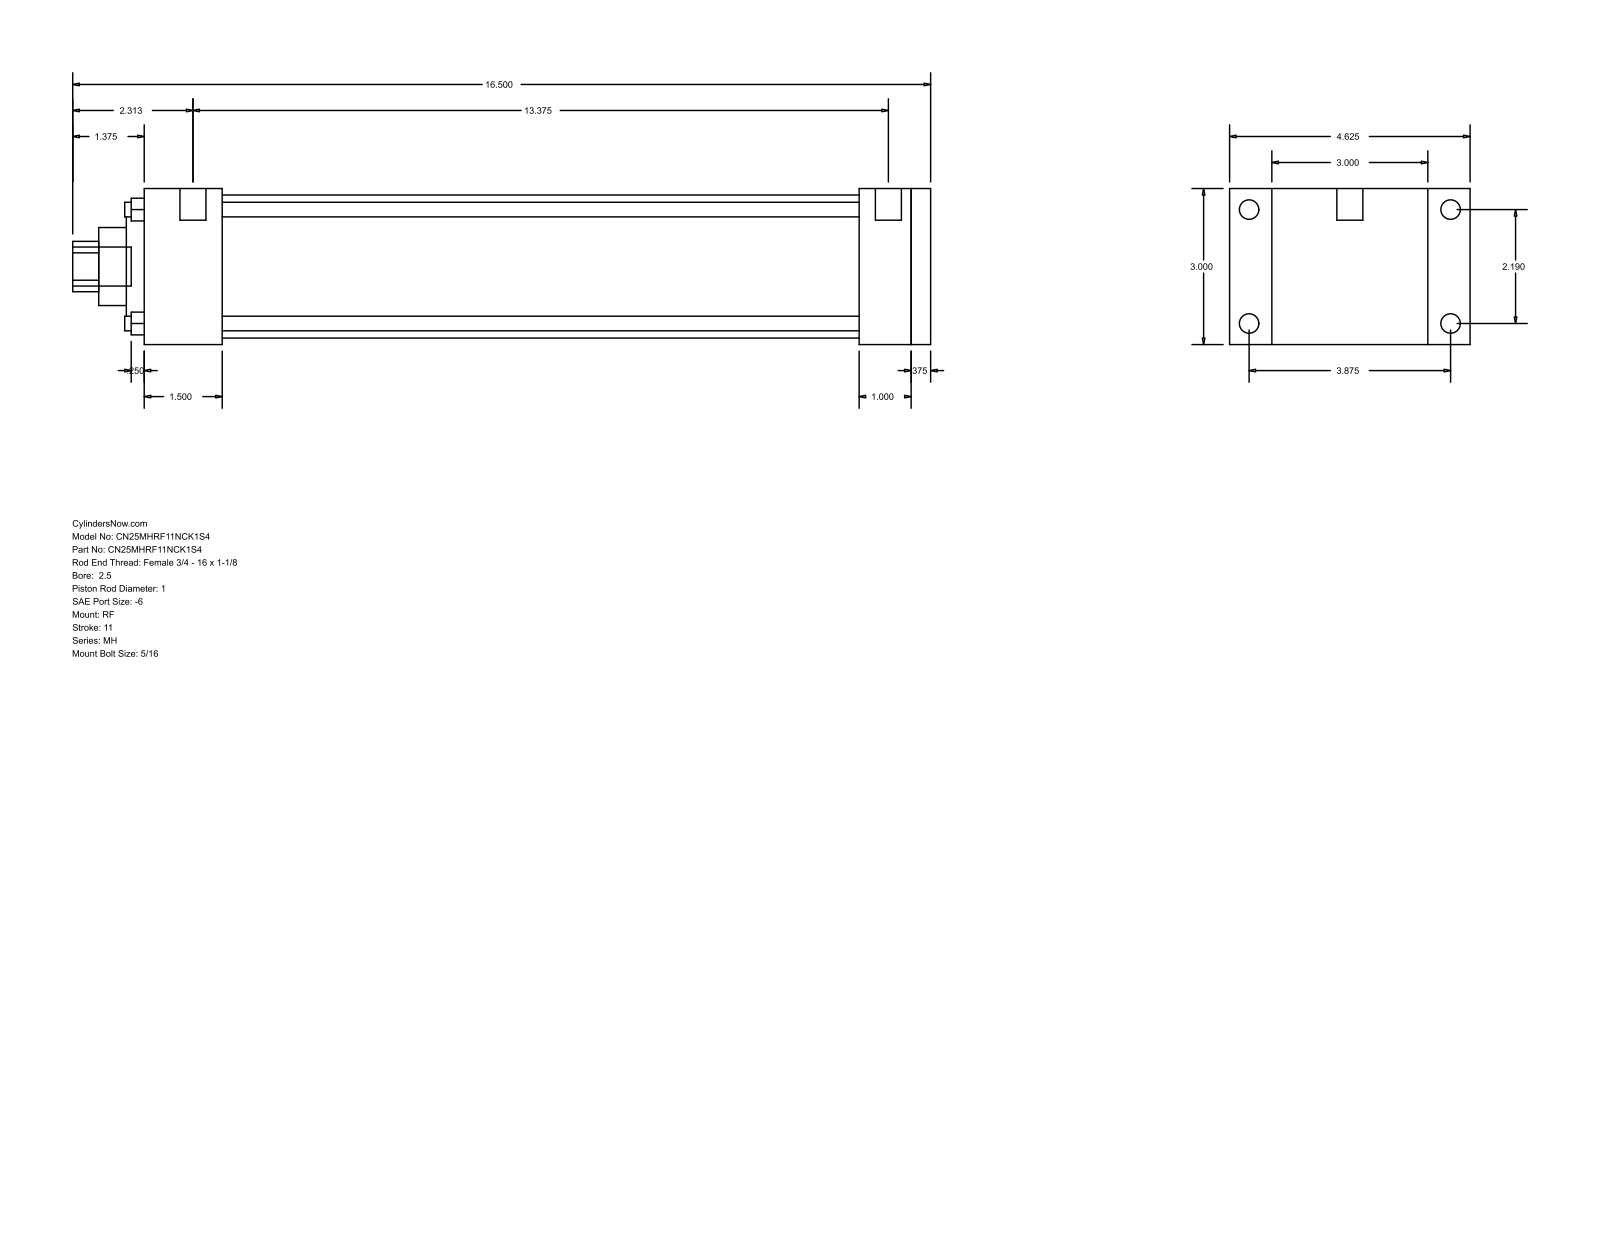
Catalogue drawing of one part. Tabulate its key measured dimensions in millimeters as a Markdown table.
| quantity | value |
| --- | --- |
| part name | MH_RF__0250_1 |
| STEP written by | GSSL Pune (CONFIG_CONTROL_DESIGN) |
| units | millimeters |
| bodies | 0 solids, 94 faces (65 planar, 29 cylindrical, 0 other) |
| overall size | 419.1 × 117.47 × 76.2 |
| round holes (diameter × count) | 7.14 × 4, 25.4 × 1, 38.1 × 1, 60.33 × 1, 69.85 × 1 |
| round bosses / shafts (diameter × count) | 9.53 × 4, 5.56 × 4, 12.7 × 2, 19.05 × 1 |
| partial cylindrical surfaces (radius × count) | 12.29 × 1 |
| main face-to-face distances | 76.2, 9.53, 384.18, 374.65, 34.92, 25.39, 349.26, 38.11, 311.15, 336.54 |
| hole center spacings | 39.33, 55.62, 78.66 |
